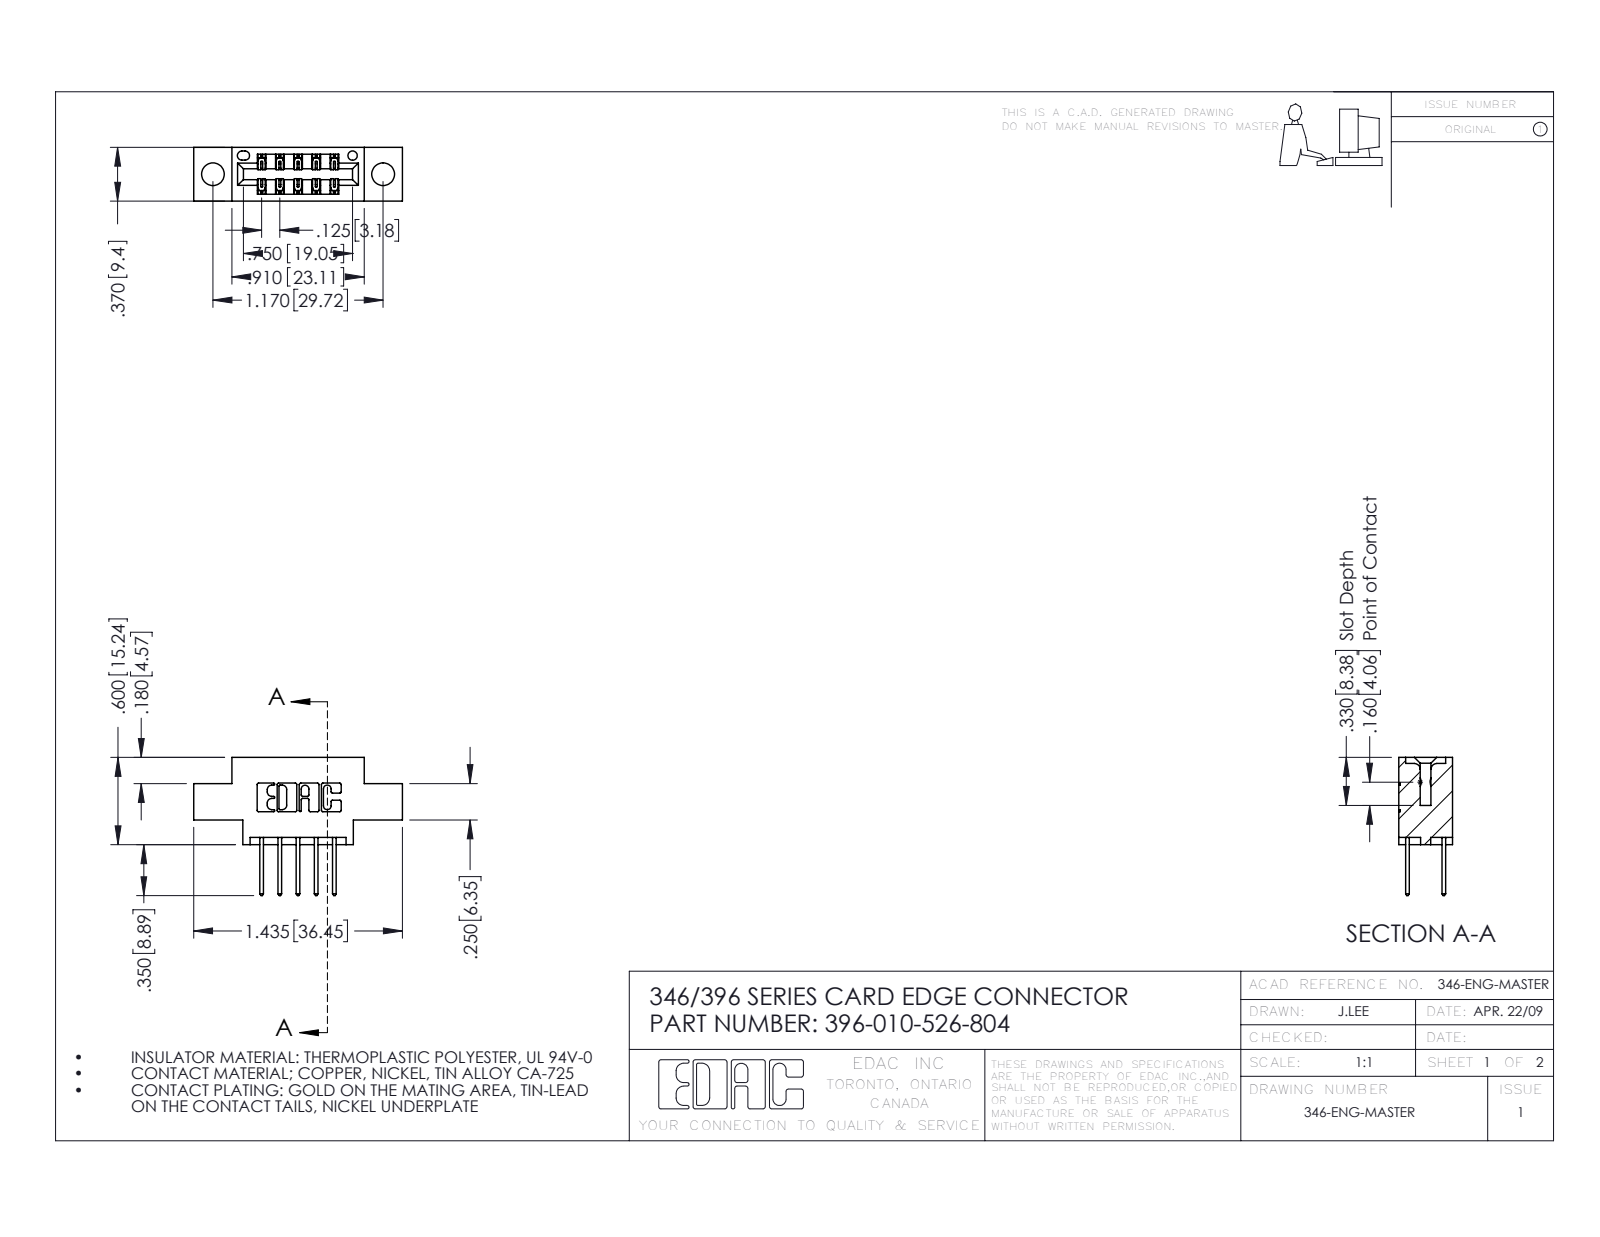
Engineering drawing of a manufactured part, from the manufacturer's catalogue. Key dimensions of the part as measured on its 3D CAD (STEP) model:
Part name (STEP PRODUCT): 346 Part_0.170 Offset - 0.156 Dia-TH; 396-010-526-804; 345-292-001_345-293-126
STEP written by: SolidWorks 2016 (CONFIG_CONTROL_DESIGN)
Units: inches
Bodies: 11 solids, 646 faces (430 planar, 216 cylindrical, 0 other)
Overall size (bounding box): 1.435 × 0.95 × 0.37
Volume: 0.186 in³ · Surface area: 5.68 in²
Round holes (diameter × count): ⌀0.156 ×2, ⌀0.064 ×1
Partial cylindrical surfaces — rounded edges, fillets, slot ends (radius × count): R0.01 ×22, R0.006 ×15, R0.01 ×10, R0.007 ×6, R0.031 ×6, R0.026 ×3, R0.014 ×2, R0.022 ×2
Main face-to-face distances: 0.25, 0.37, 0.048, 0.322, 0.025, 0.072, 0.298, 0.275, 0.225, 0.148
Hole centre spacings: 0.246, 0.969, 1.17
